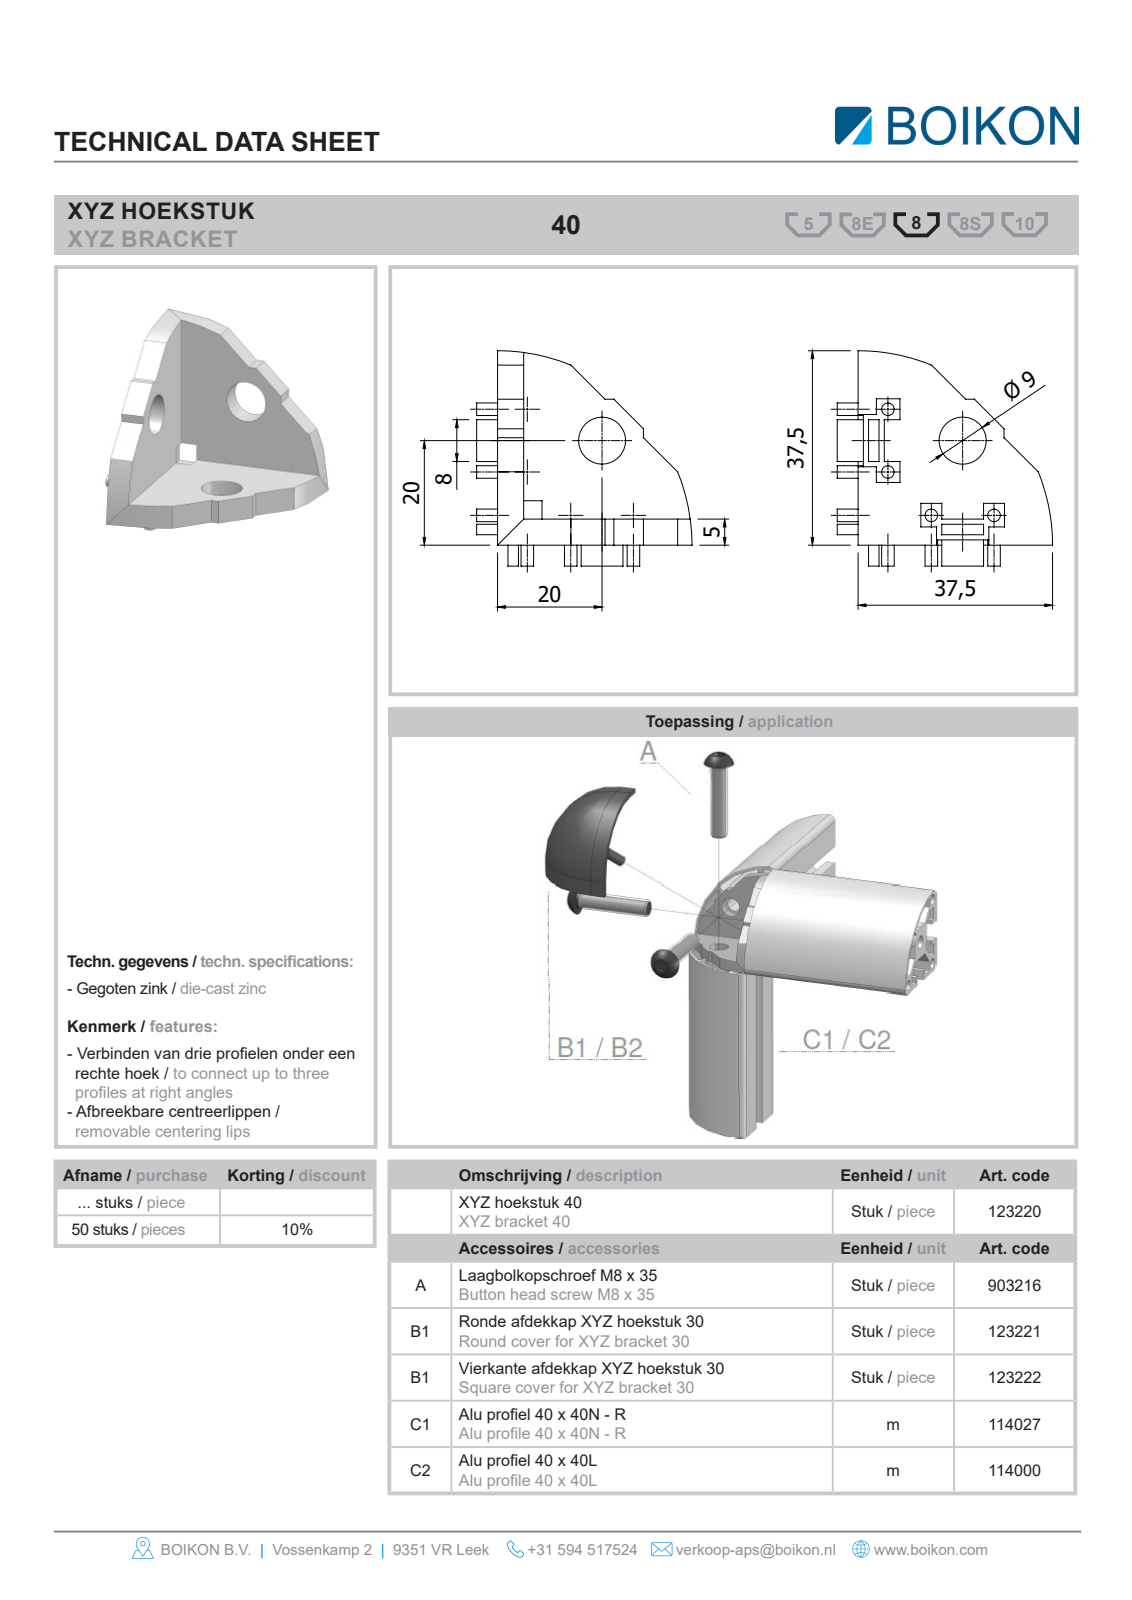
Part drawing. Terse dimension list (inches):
name: Root; 123220XYZ HOEKSTUK 40BOIKON; 120075Laagbolkopschroef M8 x 35BOIKON0
written by: HiCAD 2013 1802.4 Build 509 (AUTOMOTIVE_DESIGN)
unit: in
bodies: 4 solids, 212 faces (164 planar, 42 cylindrical, 6 other)
size: 2.646 × 2.646 × 2.646
volume: 1.026 in³; area: 16.86 in²
holes: 3× ⌀0.354
bosses: 12× ⌀0.094, 3× ⌀0.315, 3× ⌀0.255
rounds: 3× R1.465
face distances: 0.197, 0.157, 0.039, 0.118, 0.079, 0.315, 0.059, 0.236, 0.256, 0.098
